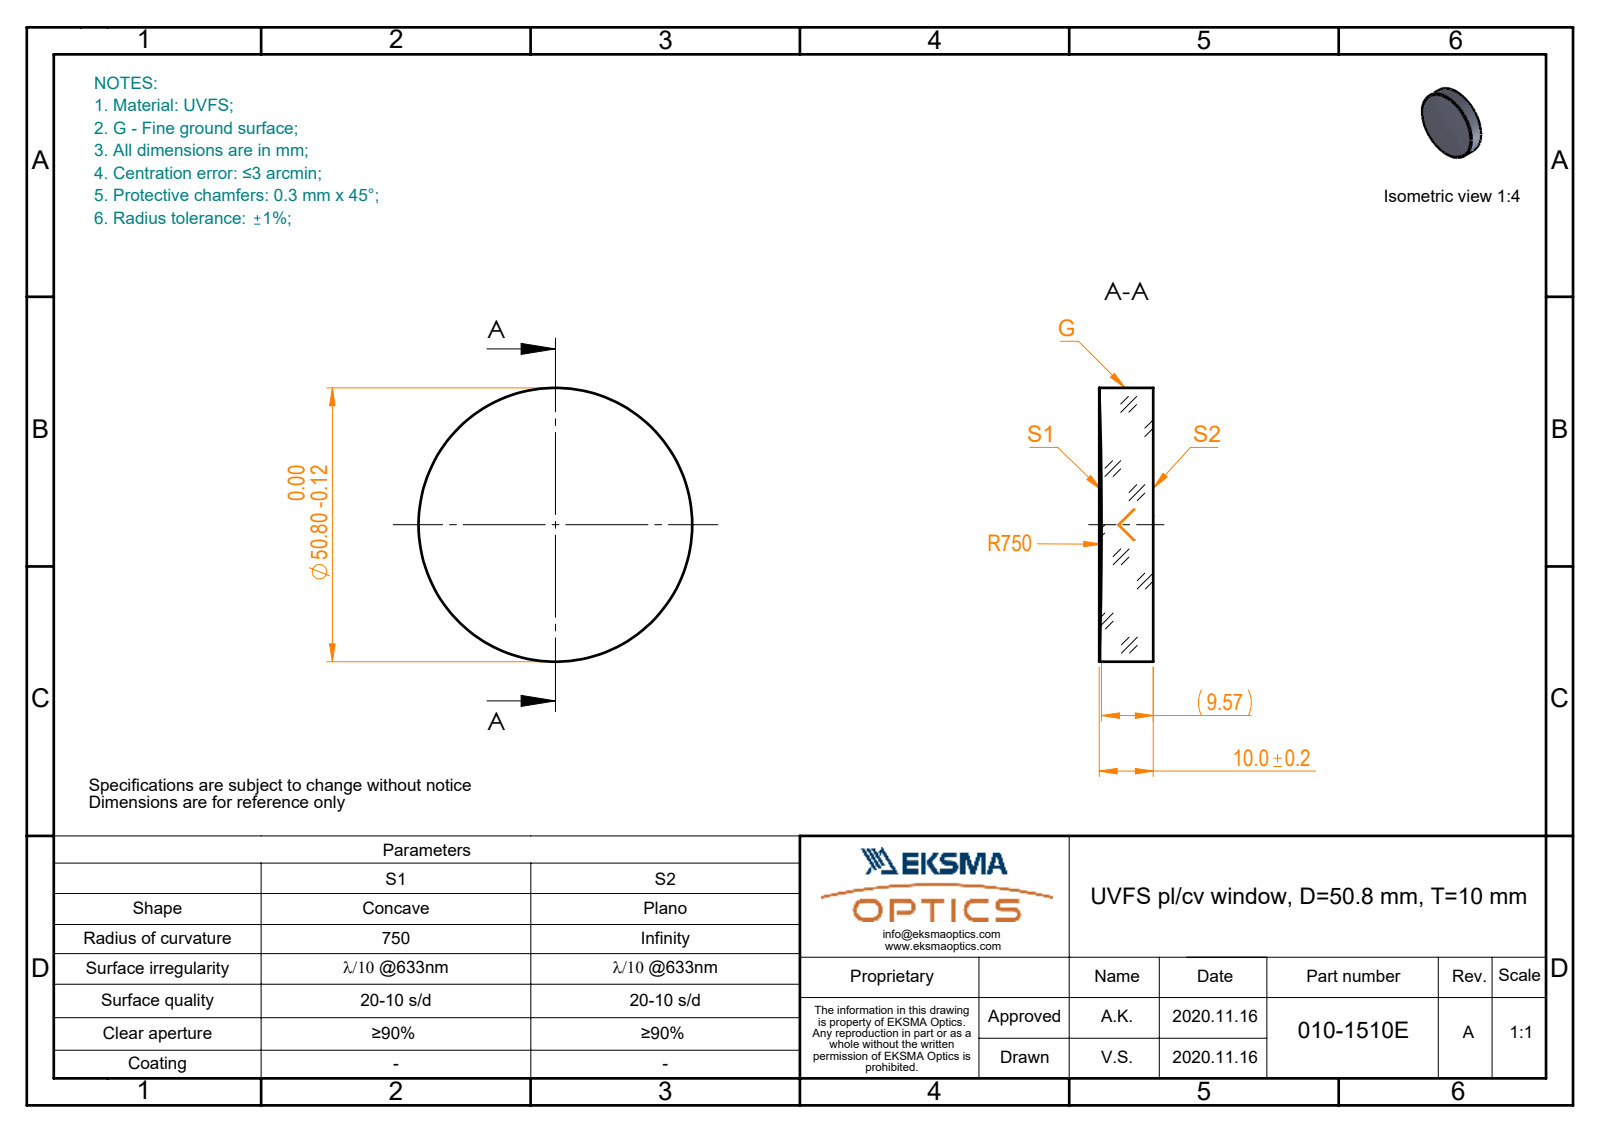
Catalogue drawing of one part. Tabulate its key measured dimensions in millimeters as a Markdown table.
| quantity | value |
| --- | --- |
| part name | 010-1510E_UVFS_PCV_window |
| STEP written by | SolidWorks 2019 (CONFIG_CONTROL_DESIGN) |
| units | millimeters |
| bodies | 1 solid, 5 faces (1 planar, 2 cylindrical, 2 other) |
| overall size | 50.8 × 50.8 × 10 |
| volume | 19 832 mm³ |
| surface area | 5 650 mm² |
| round bosses / shafts (diameter × count) | 50.8 × 1 |
